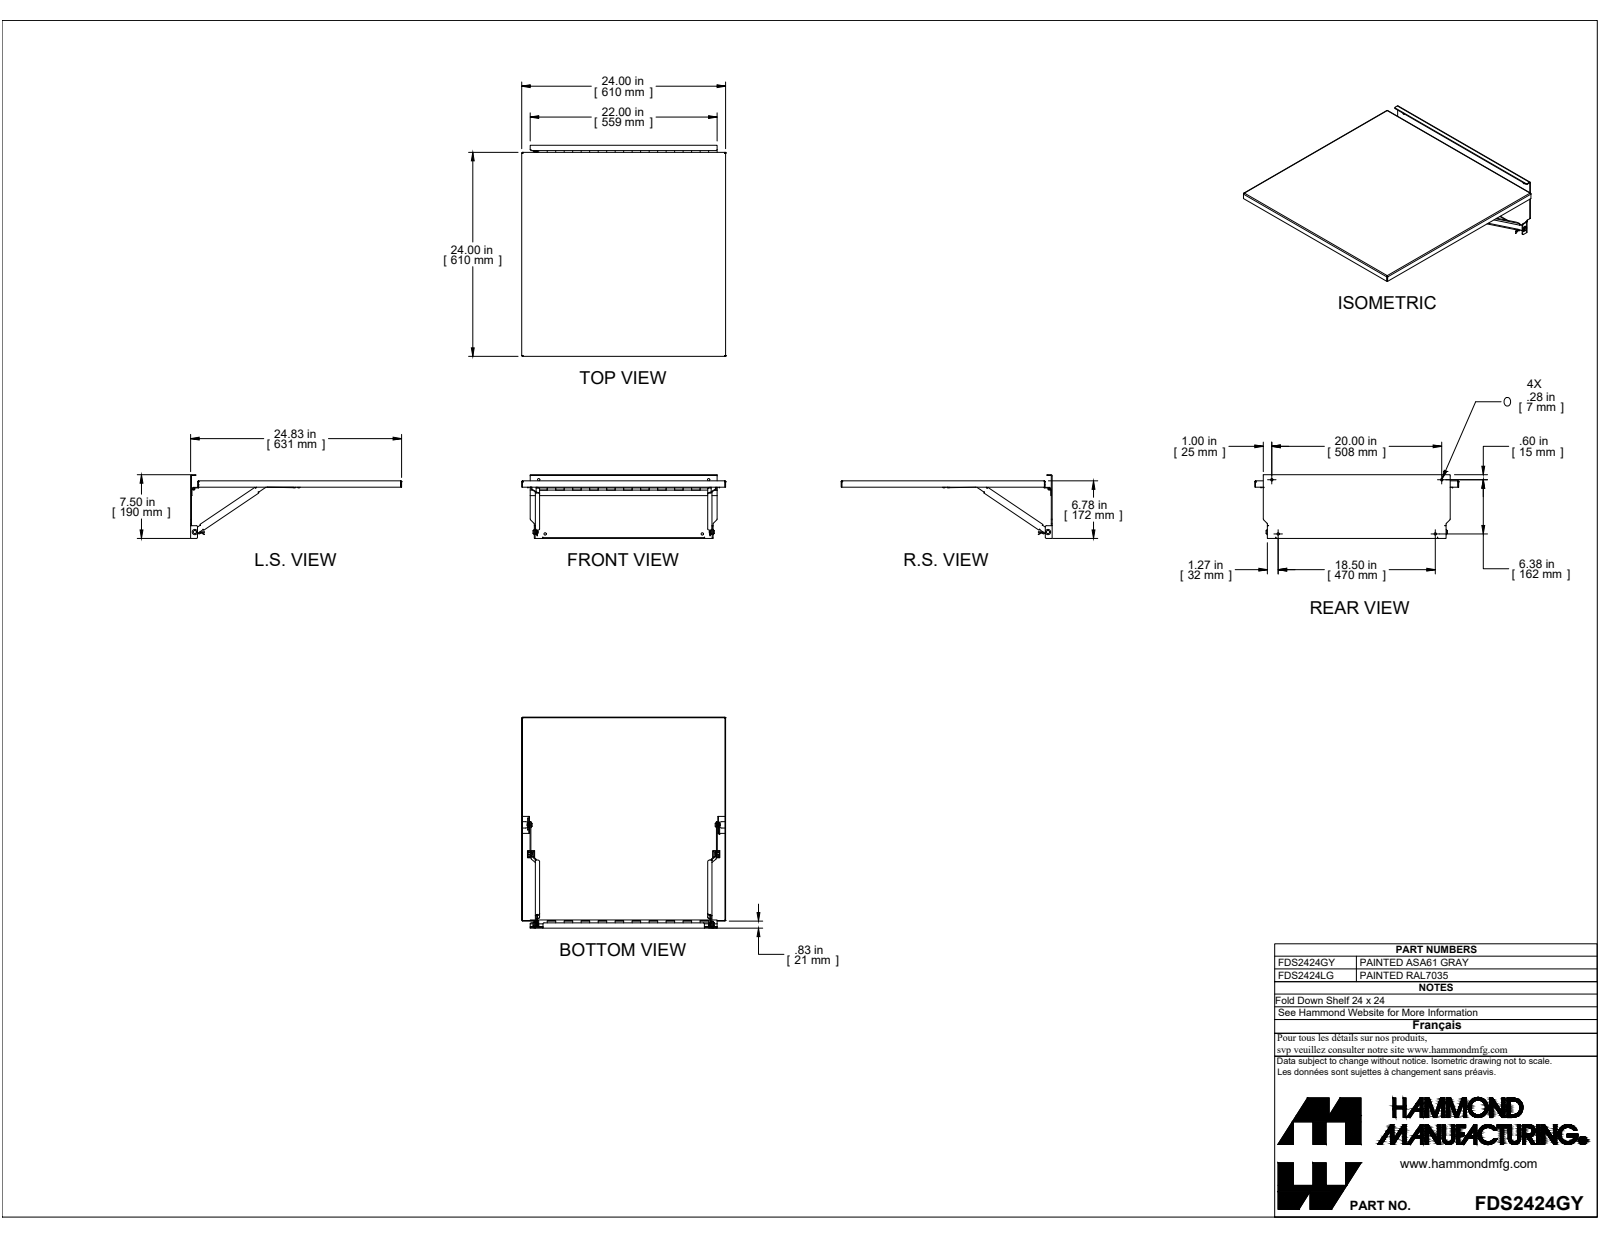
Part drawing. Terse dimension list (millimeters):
name: FDS2424LG
written by: SolidWorks 2019 (CONFIG_CONTROL_DESIGN)
unit: mm
bodies: 38 solids, 581 faces (355 planar, 194 cylindrical, 32 other)
size: 630.7 × 609.6 × 190.5
volume: 1 162 000 mm³; area: 1 205 000 mm²
holes: 4× ⌀2.4, 4× ⌀7.1, 3× ⌀6.6, 2× ⌀3.2, 2× ⌀6.5, 2× ⌀6.7, 2× ⌀6.7, 2× ⌀7.2, 1× ⌀4.7, 1× ⌀5.1
bosses: 3× ⌀13, 3× ⌀6.4, 2× ⌀12.7, 1× ⌀15.9, 1× ⌀15.9, 1× ⌀9.5, 1× ⌀9.5, 1× ⌀8.1
rounds: 21× R6.4, 12× R1.2, 12× R3.6, 10× R3.2, 6× R0.9, 6× R2.7, 2× R1.3, 2× R9.5
face distances: 1.8, 2.4, 607.8, 605.9, 609.6, 20.5, 22.9, 15.9, 188.1, 626.5
hole spacings: 24.2, 34.7, 89.3, 146.1, 156.4, 157.6, 163, 493.5
